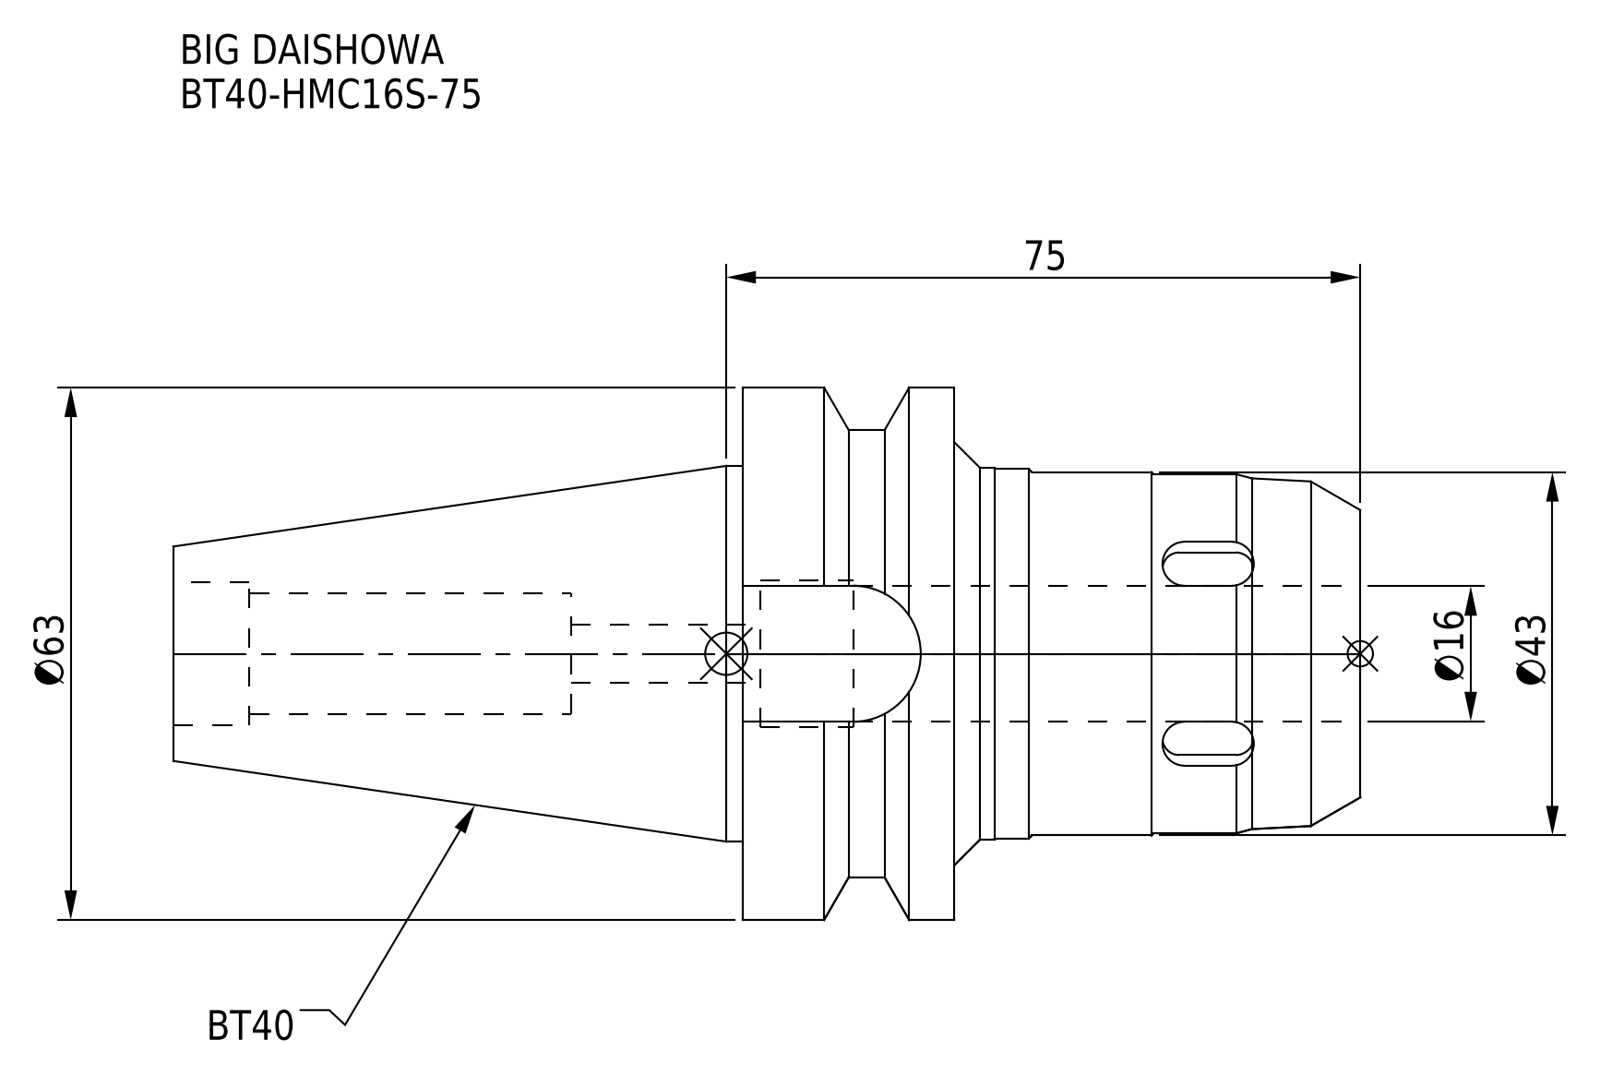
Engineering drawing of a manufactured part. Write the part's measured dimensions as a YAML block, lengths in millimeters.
part_name: "BT40-HMC16S-75"
step_written_by: "CREO PARAMETRIC BY PTC INC, 2016380 (AUTOMOTIVE_DESIGN)"
units: millimeters
bodies: {solids: 1, faces: 95, planar: 33, cylindrical: 40, other: 22}
overall_size: [140.4, 63, 63]
volume: 177509
surface_area: 31005
round_holes:
  - {diameter: 6.8, count: 1}
  - {diameter: 14.2, count: 1}
  - {diameter: 16, count: 1}
  - {diameter: 17, count: 1}
  - {diameter: 17.4, count: 1}
round_bosses_or_shafts:
  - {diameter: 63, count: 1}
  - {diameter: 53, count: 1}
  - {diameter: 44.45, count: 1}
  - {diameter: 44, count: 1}
  - {diameter: 43.7, count: 1}
  - {diameter: 43, count: 1}
  - {diameter: 42.5, count: 1}
partial_cylinders:
  - {radius: 3, count: 6}
  - {radius: 8.05, count: 1}
face_to_face_distances: [25, 48, 73, 45, 140.4, 92.4, 67.4, 38, 71, 23]
